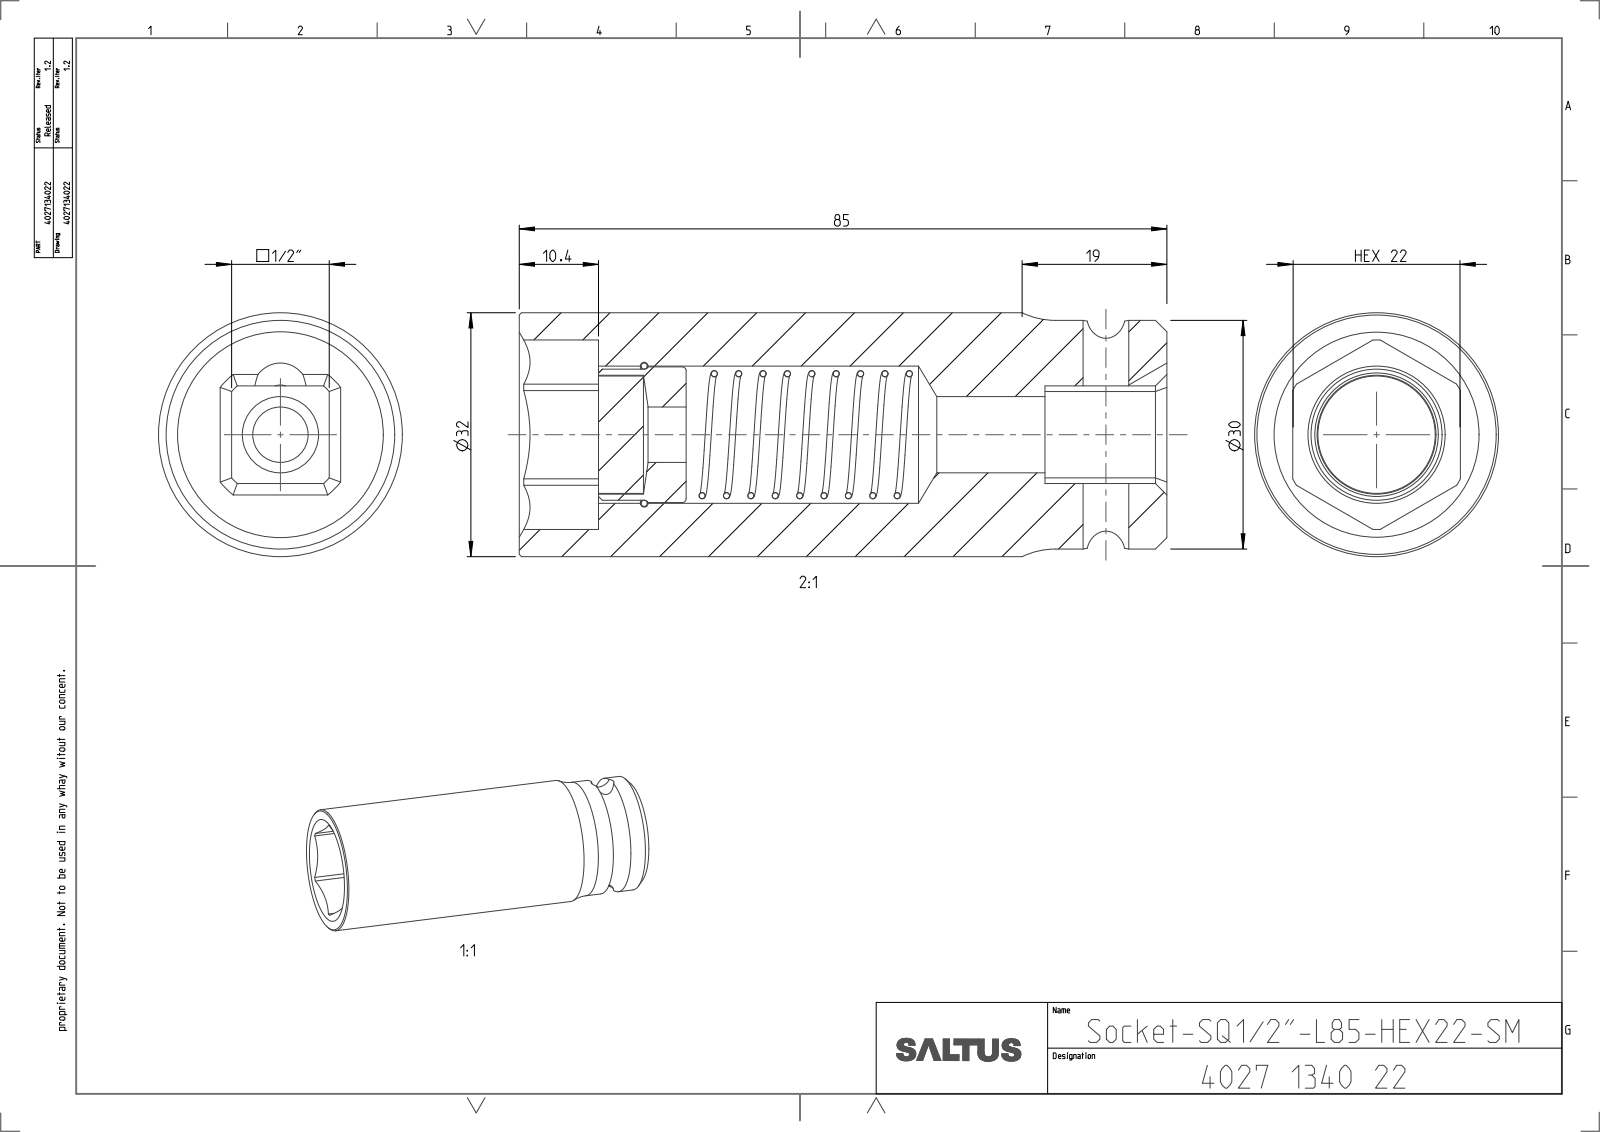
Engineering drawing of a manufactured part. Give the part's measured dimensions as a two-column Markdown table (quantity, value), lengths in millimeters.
| quantity | value |
| --- | --- |
| part name | 4027134022 |
| STEP written by | CREO PARAMETRIC BY PTC INC, 2022414 (CONFIG_CONTROL_DESIGN) |
| units | millimeters |
| bodies | 5 solids, 99 faces (26 planar, 37 cylindrical, 36 other) |
| overall size | 85 × 32 × 32 |
| volume | 48 860 mm³ |
| surface area | 17 739 mm² |
| round holes (diameter × count) | 6 × 1, 7.27 × 1, 10 × 1, 15.6 × 1, 18 × 1 |
| round bosses / shafts (diameter × count) | 32 × 1, 30 × 1, 17.8 × 1, 17.2 × 1, 15.4 × 1 |
| partial cylindrical surfaces (radius × count) | 4 × 1, 8.55 × 1, 12.43 × 1 |
| main face-to-face distances | 22, 74.6, 12.82, 4.59, 17.41, 85, 10.4, 68.7, 5.9, 16.3 |
